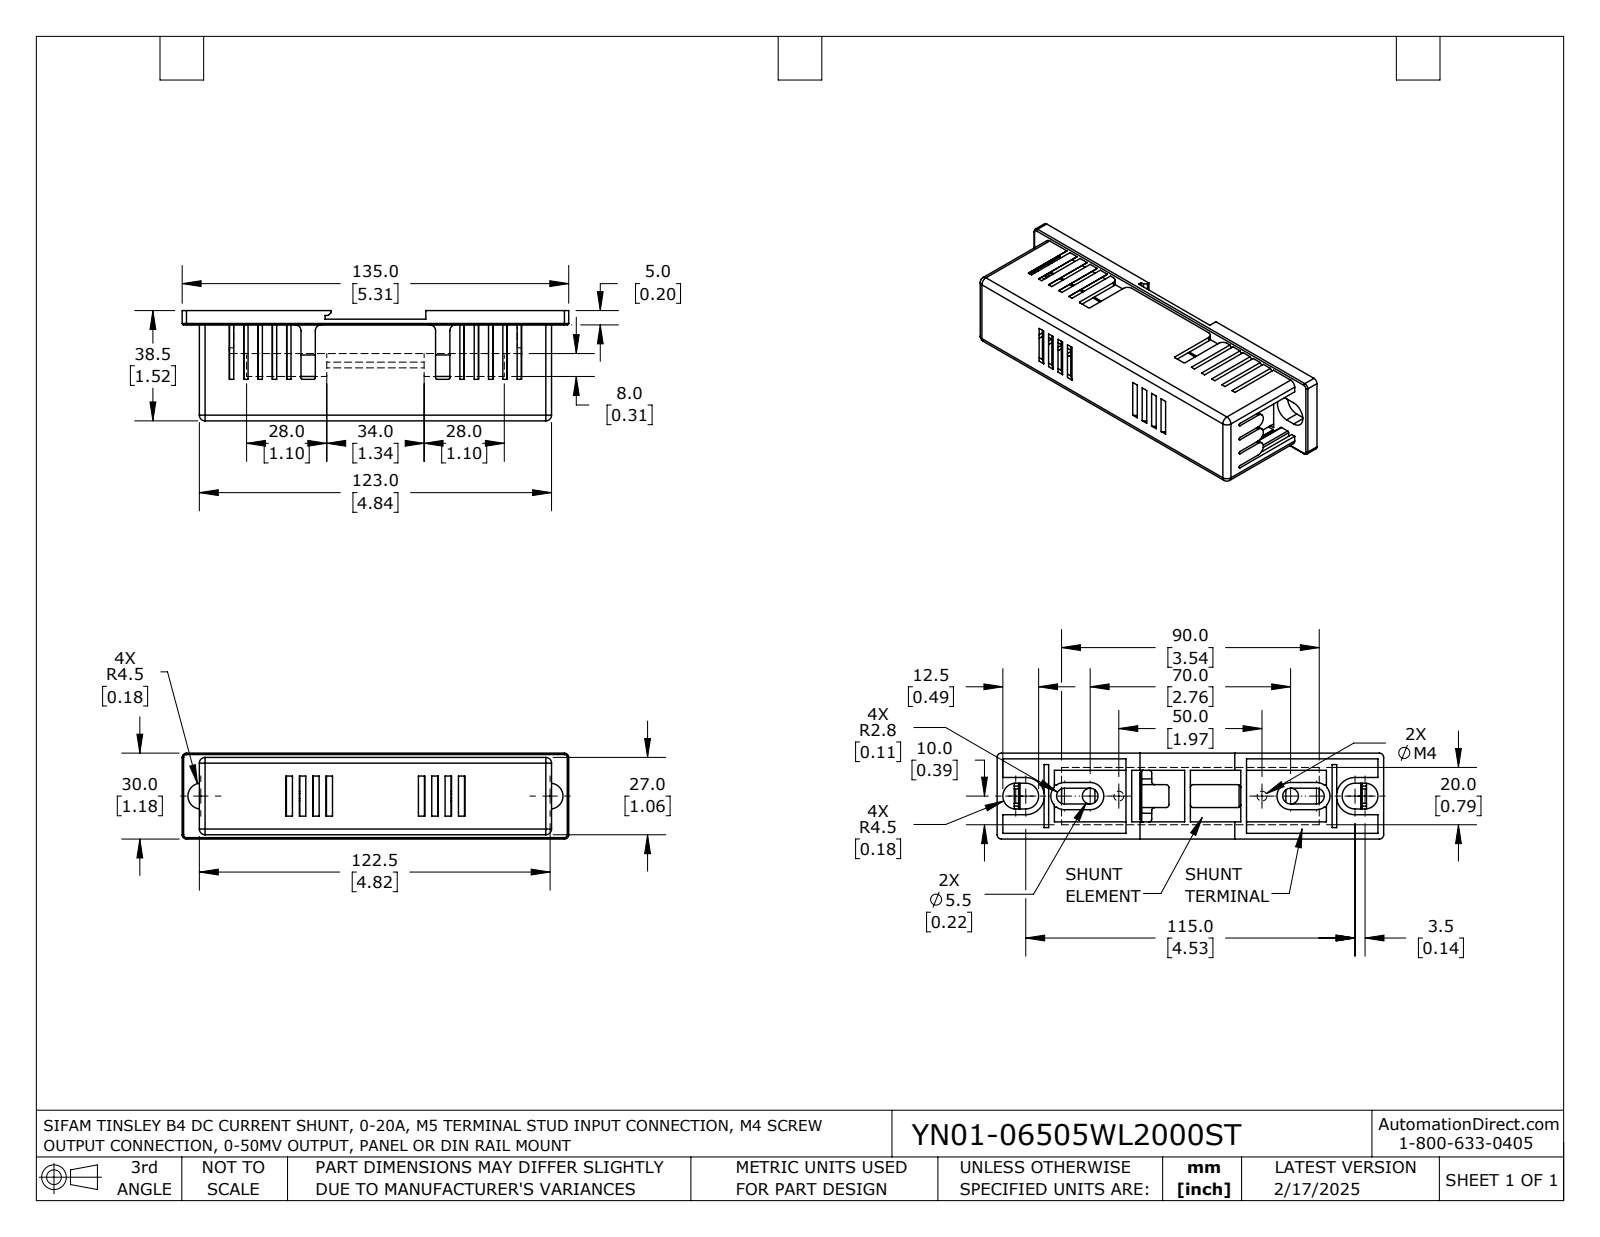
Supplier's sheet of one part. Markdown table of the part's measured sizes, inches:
| quantity | value |
| --- | --- |
| part name | YN01-06505WL2000ST |
| STEP written by | SolidWorks 2021 (AUTOMOTIVE_DESIGN) |
| units | inches |
| bodies | 2 solids, 505 faces (326 planar, 143 cylindrical, 36 other) |
| overall size | 5.315 × 1.516 × 1.181 |
| volume | 2.433 in³ |
| surface area | 70.68 in² |
| round holes (diameter × count) | 0.079 × 2, 0.135 × 2, 0.217 × 2 |
| partial cylindrical surfaces (radius × count) | 0.02 × 38, 0.039 × 16, 0.079 × 12, 0.059 × 4, 0.177 × 4, 0.187 × 4, 0.098 × 3, 0.108 × 2 |
| main face-to-face distances | 0.059, 1.004, 0.945, 0.079, 0.039, 1.063, 0.118, 0.886, 0.906, 0.787 |
| hole center spacings | 0.394, 2.362, 1.969, 2.756 |
